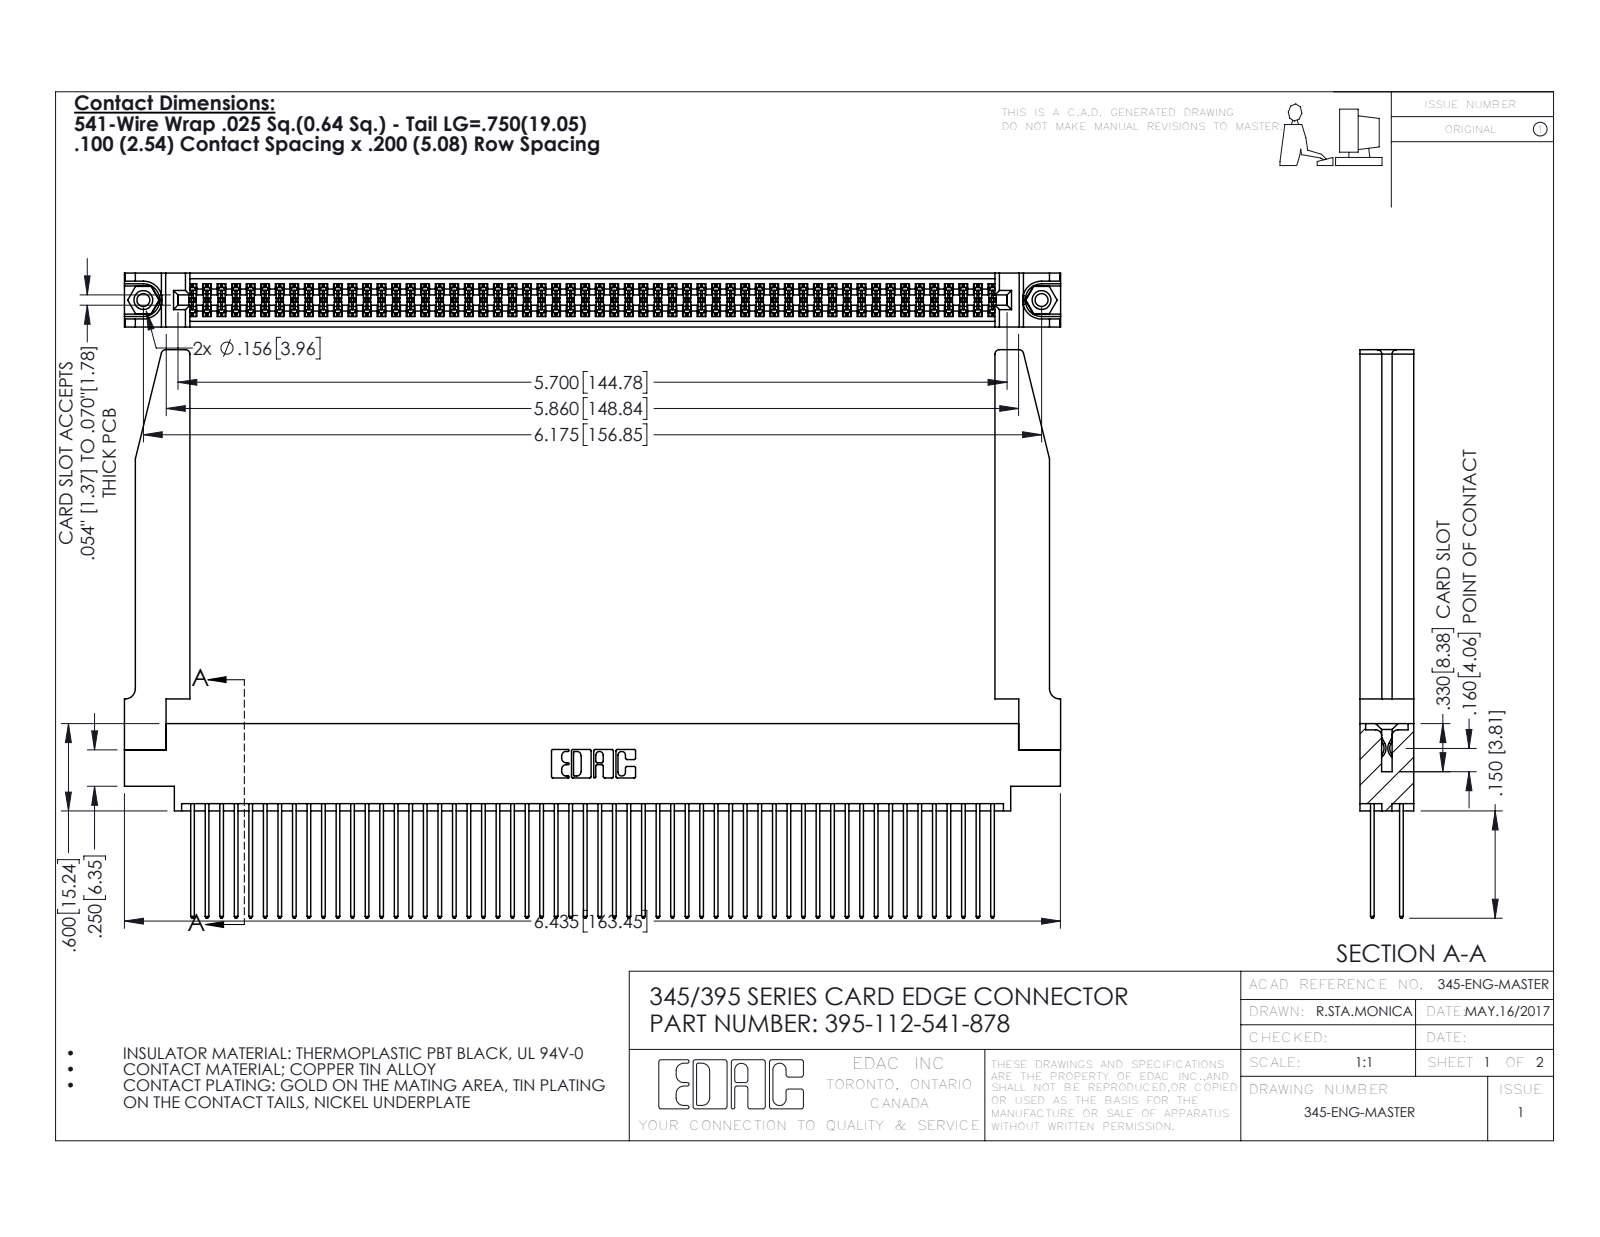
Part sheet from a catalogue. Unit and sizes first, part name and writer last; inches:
Units: inches
Overall size (bounding box): 6.436 × 3.907 × 0.37
Round holes (diameter × count): ⌀0.089 ×2, ⌀0.125 ×2, ⌀0.156 ×2, ⌀0.064 ×1
Round bosses / shafts (diameter × count): ⌀0.155 ×2
Partial cylindrical surfaces — rounded edges, fillets, slot ends (radius × count): R0.006 ×168, R0.01 ×112, R0.01 ×22, R0.03 ×8, R0.007 ×6, R0.031 ×6, R0.026 ×3, R0.014 ×2
Main face-to-face distances: 0.072, 0.298, 0.37, 0.098, 0.272, 0.025, 0.2, 0.225, 0.175, 0.148
Hole centre spacings: 0.27, 5.939, 6.175
Volume: 1.483 in³ · Surface area: 53.82 in²
Bodies: 117 solids, 5964 faces (3922 planar, 1990 cylindrical, 52 other)
Part name (STEP PRODUCT): 345-292-001_345-293-141; 395-112-541-878; 345-250-001_345-250-001-102; 345-220-078_345-220-078 (+1 more)
STEP written by: SolidWorks 2016 (CONFIG_CONTROL_DESIGN)
